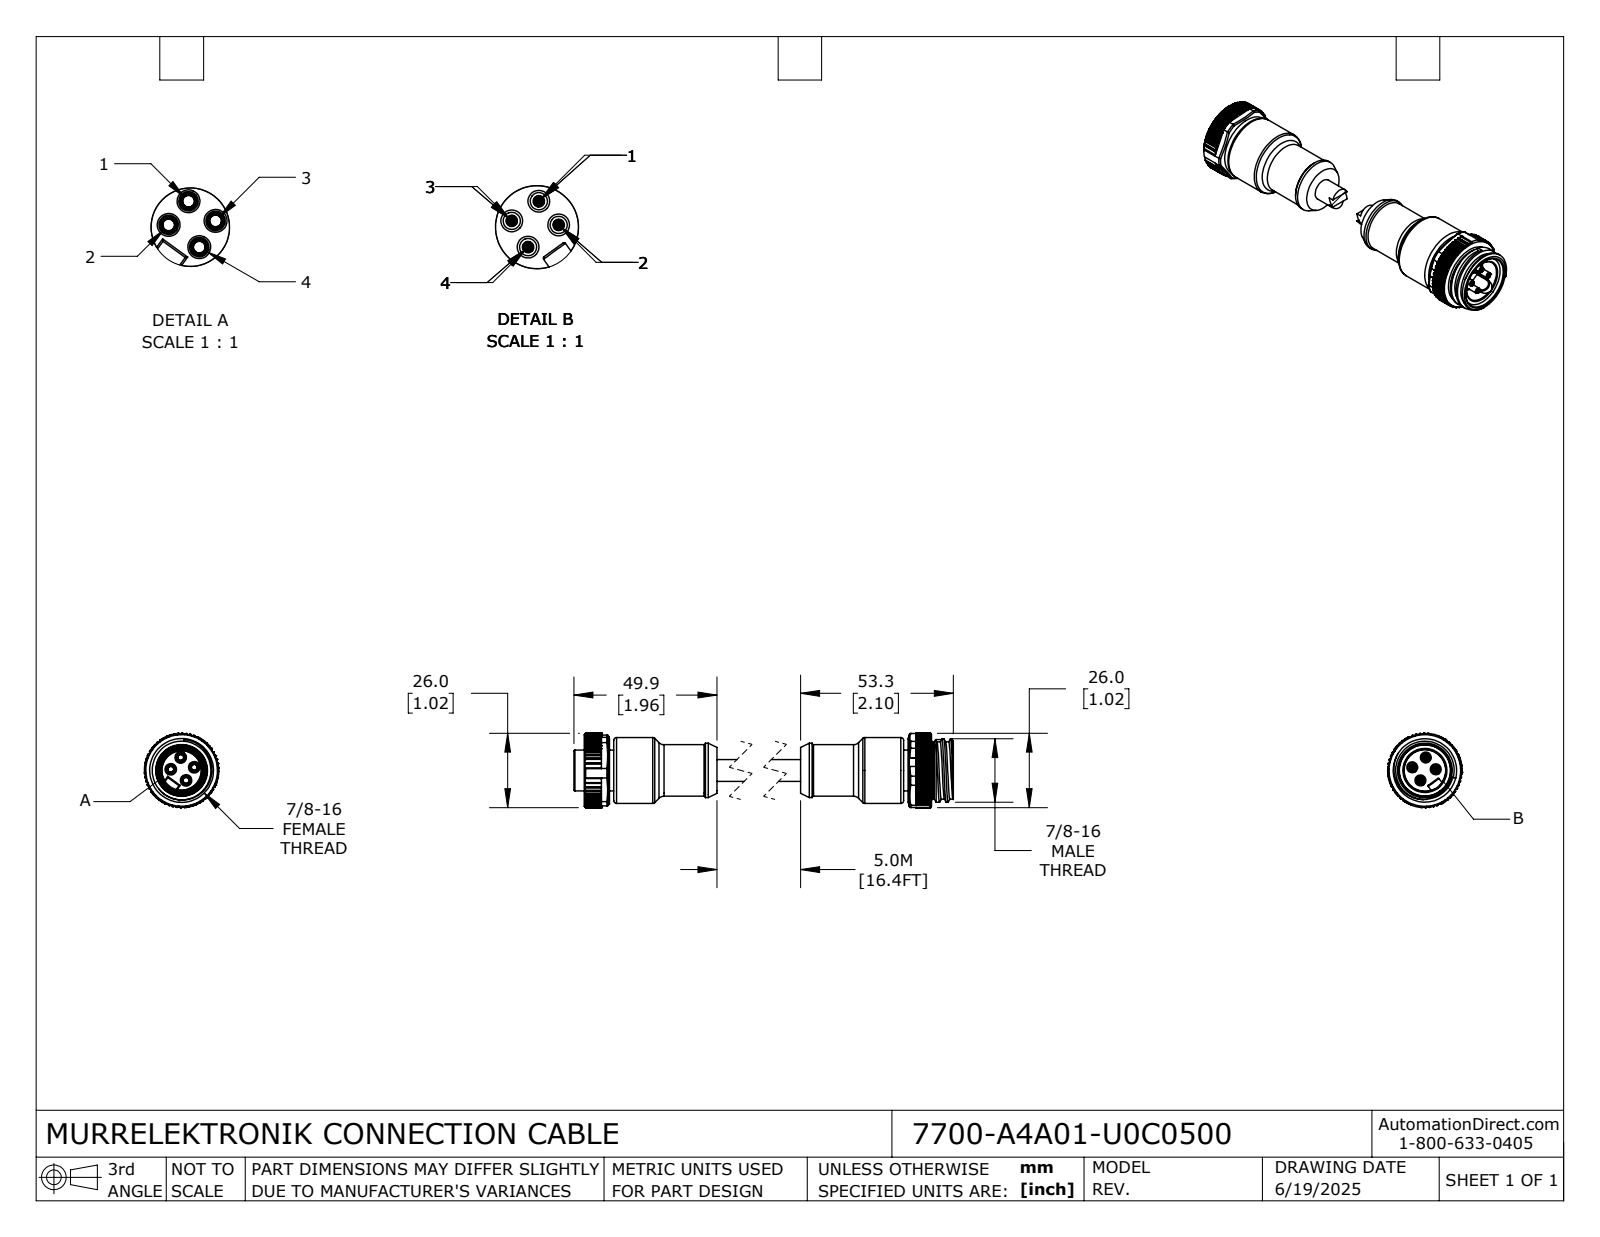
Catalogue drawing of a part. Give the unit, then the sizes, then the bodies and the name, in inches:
Units: inches
Overall size (bounding box): 5.244 × 1.024 × 1.024
Round holes (diameter × count): ⌀0.081 ×4, ⌀0.118 ×4, ⌀0.134 ×4, ⌀0.61 ×1, ⌀0.614 ×1, ⌀0.728 ×1, ⌀0.807 ×1, ⌀0.875 ×1
Round bosses / shafts (diameter × count): ⌀0.079 ×4, ⌀0.906 ×1, ⌀0.873 ×1, ⌀0.789 ×1, ⌀0.787 ×1, ⌀0.748 ×1, ⌀0.713 ×1, ⌀0.709 ×1
Partial cylindrical surfaces — rounded edges, fillets, slot ends (radius × count): R0.008 ×252, R0.012 ×18, R0.004 ×8, R0.027 ×4, R0.029 ×4, R0.093 ×1, R0.512 ×1
Main face-to-face distances: 0.059, 4.075, 1.476, 2.657, 1.417, 2.598, 4.134, 0.346, 4.421, 0.287
Hole centre spacings: 0.15, 0.324, 0.179, 0.179, 0.212, 0.213, 0.23, 0.26
Volume: 2.059 in³ · Surface area: 22.09 in²
Bodies: 2 solids, 1226 faces (520 planar, 543 cylindrical, 163 other)
Part name (STEP PRODUCT): 7700-A4A01-U0C0500_FEMALE; 7700-A4A01-U0C0500_MALE; 7700-A4A01-U0C0500
STEP written by: SolidWorks 2024 (CONFIG_CONTROL_DESIGN)
